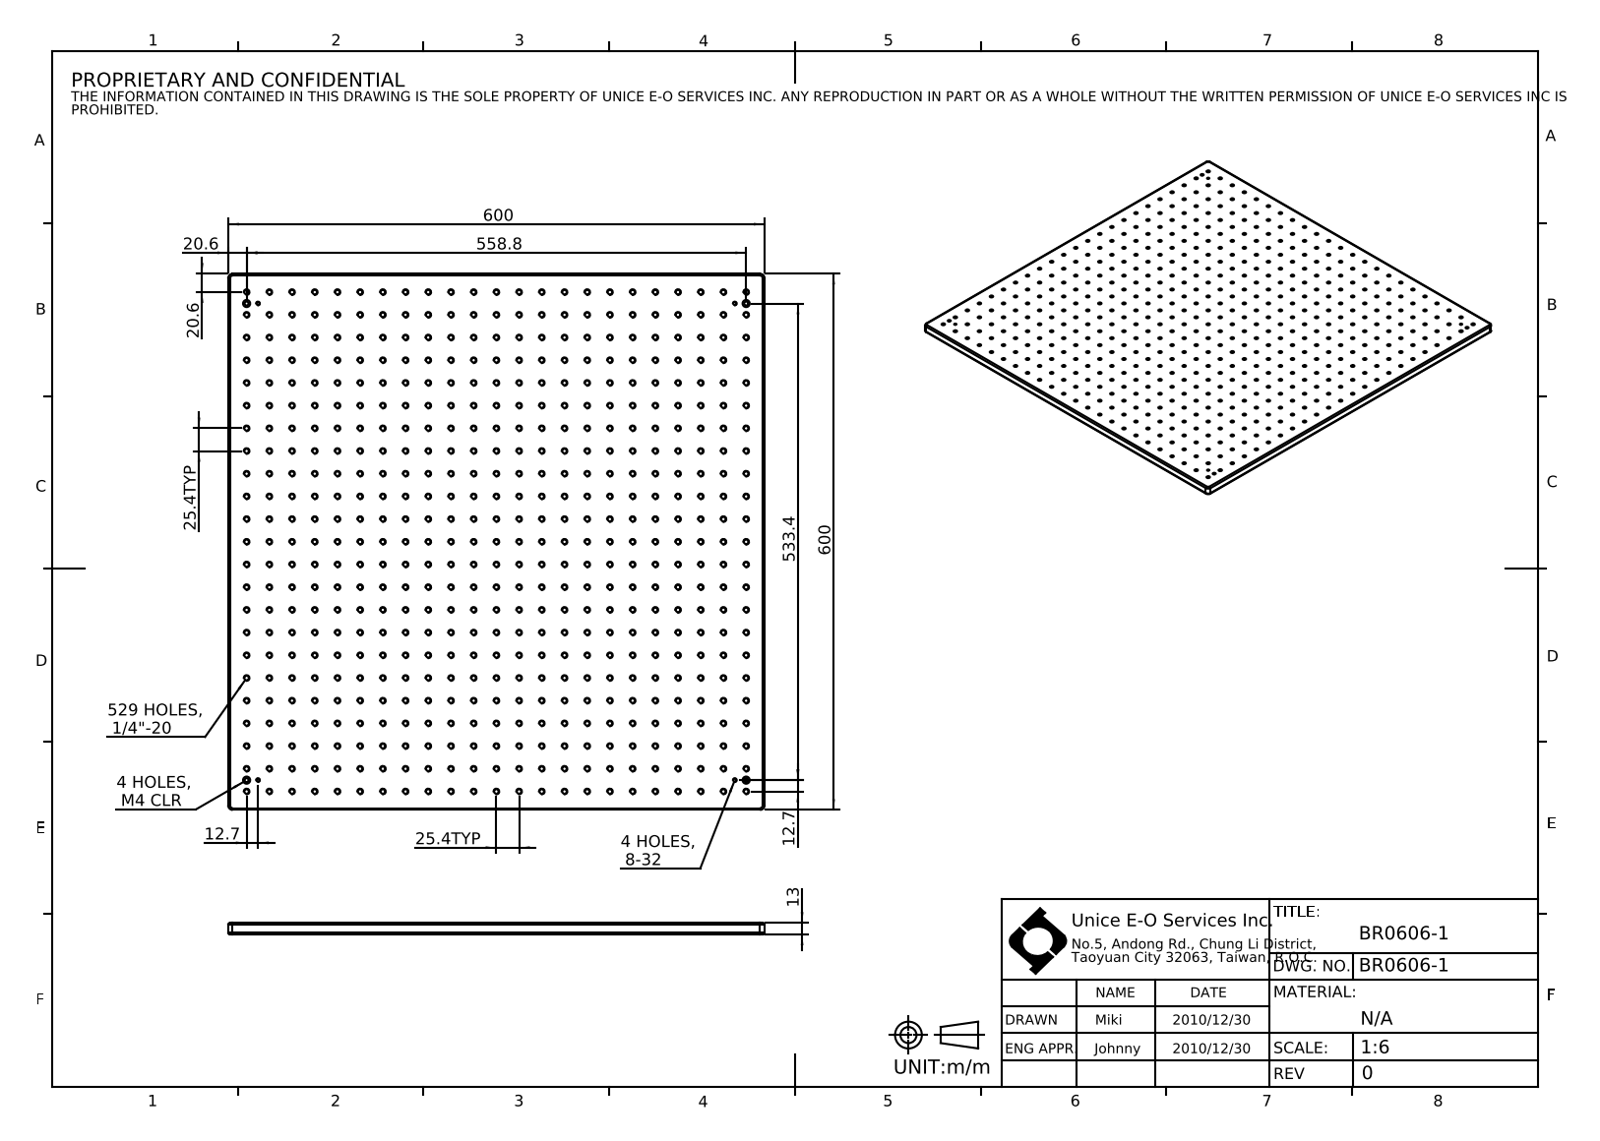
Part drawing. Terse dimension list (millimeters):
name: BR0606-1
written by: SolidWorks 2016 (CONFIG_CONTROL_DESIGN)
unit: mm
bodies: 1 solid, 1112 faces (10 planar, 1094 cylindrical, 8 other)
size: 600 × 600 × 13
volume: 4 533 000 mm³; area: 836 939 mm²
holes: 529× ⌀5.11, 4× ⌀3.45, 4× ⌀4.5, 4× ⌀8
rounds: 8× R2, 4× R5
face distances: 13, 600, 7, 6
hole spacings: 25.4, 50.8, 76.2, 101.6, 127, 152.4, 177.8, 203.2
